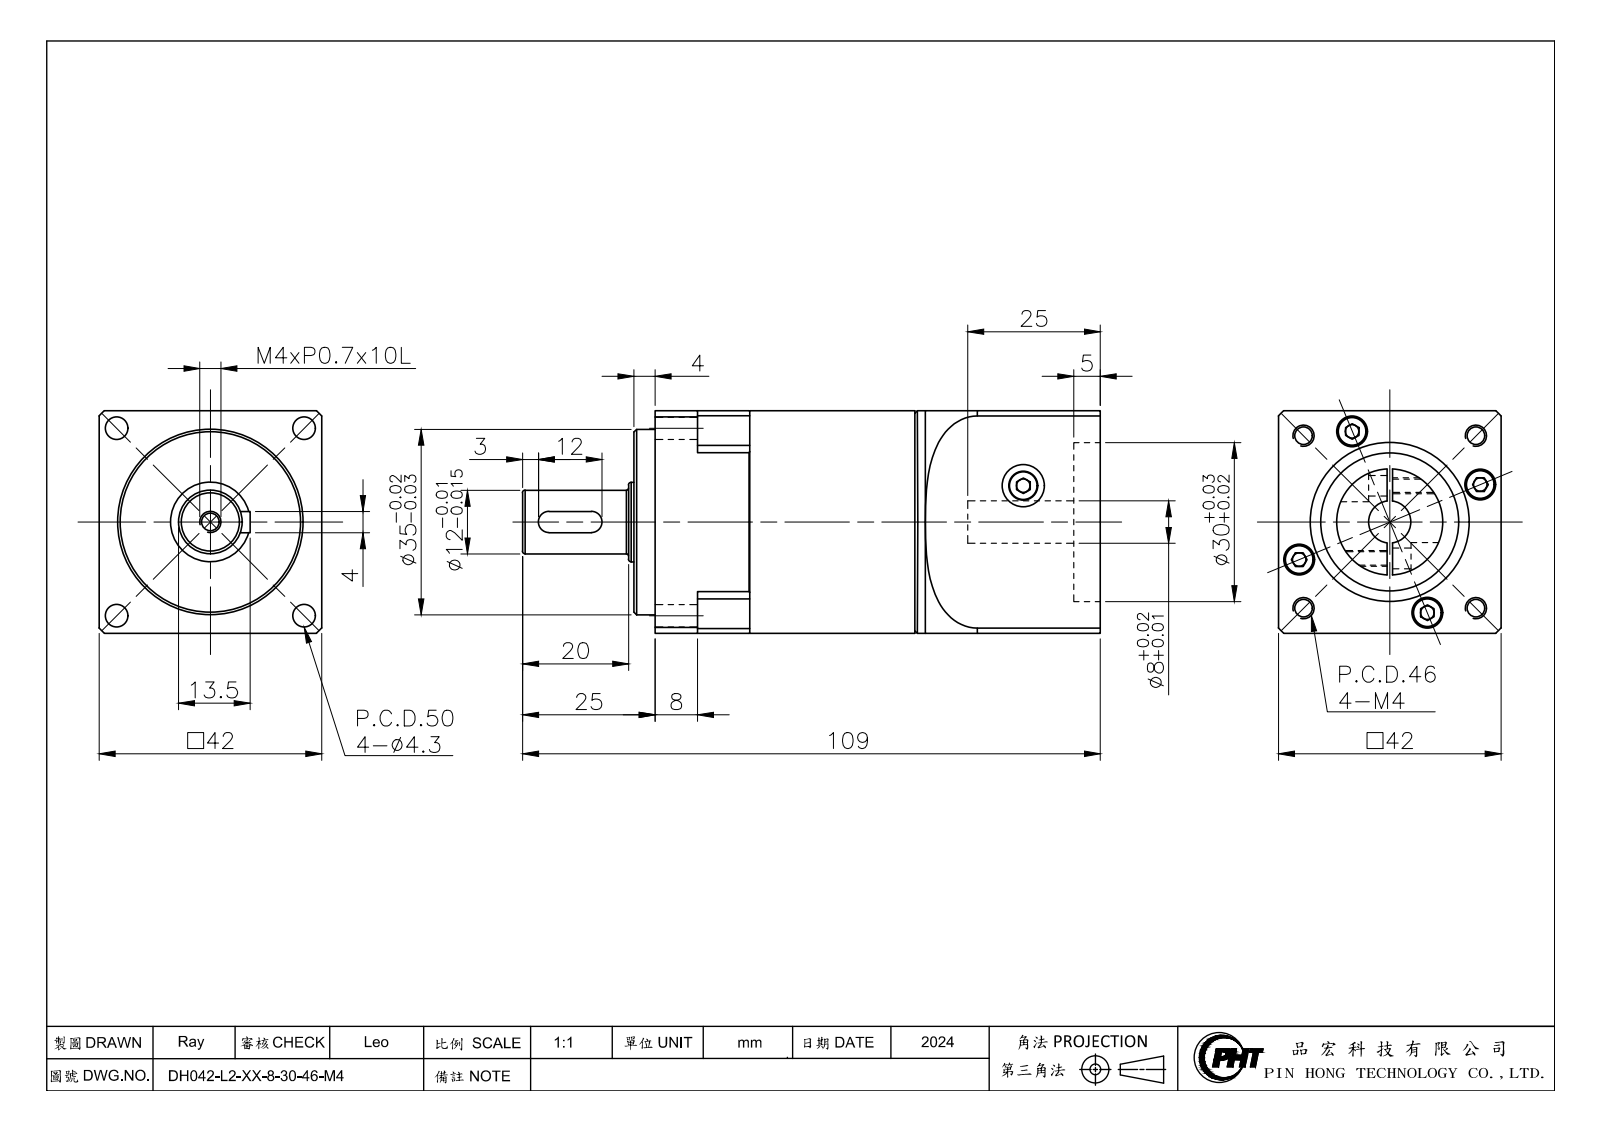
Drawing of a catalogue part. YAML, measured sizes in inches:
part_name: "DH042-L2-XX-8-30-46-M4_2024"
step_written_by: "SolidWorks 2016 (CONFIG_CONTROL_DESIGN)"
units: inches
bodies: {solids: 2, faces: 204, planar: 82, cylindrical: 98, other: 24}
overall_size: [4.291, 1.654, 1.654]
volume: 7.636
surface_area: 43.76
round_holes:
  - {diameter: 0.13, count: 9}
  - {diameter: 0.169, count: 4}
  - {diameter: 0.228, count: 4}
  - {diameter: 0.315, count: 3}
  - {diameter: 1.024, count: 1}
  - {diameter: 1.181, count: 1}
round_bosses_or_shafts:
  - {diameter: 0.217, count: 4}
  - {diameter: 1.654, count: 1}
  - {diameter: 1.378, count: 1}
  - {diameter: 0.787, count: 1}
  - {diameter: 0.591, count: 1}
  - {diameter: 0.472, count: 1}
partial_cylinders:
  - {radius: 0.157, count: 4}
  - {radius: 0.079, count: 2}
  - {radius: 0.984, count: 1}
  - {radius: 1.142, count: 1}
face_to_face_distances: [1.654, 0.157, 1.378, 3.307, 2.087, 3.465, 1.929, 3.11, 0.807, 0.846]
hole_center_spacings: [1.337, 0.079, 0.363, 0.418, 0.728, 0.906, 0.919, 0.975]
